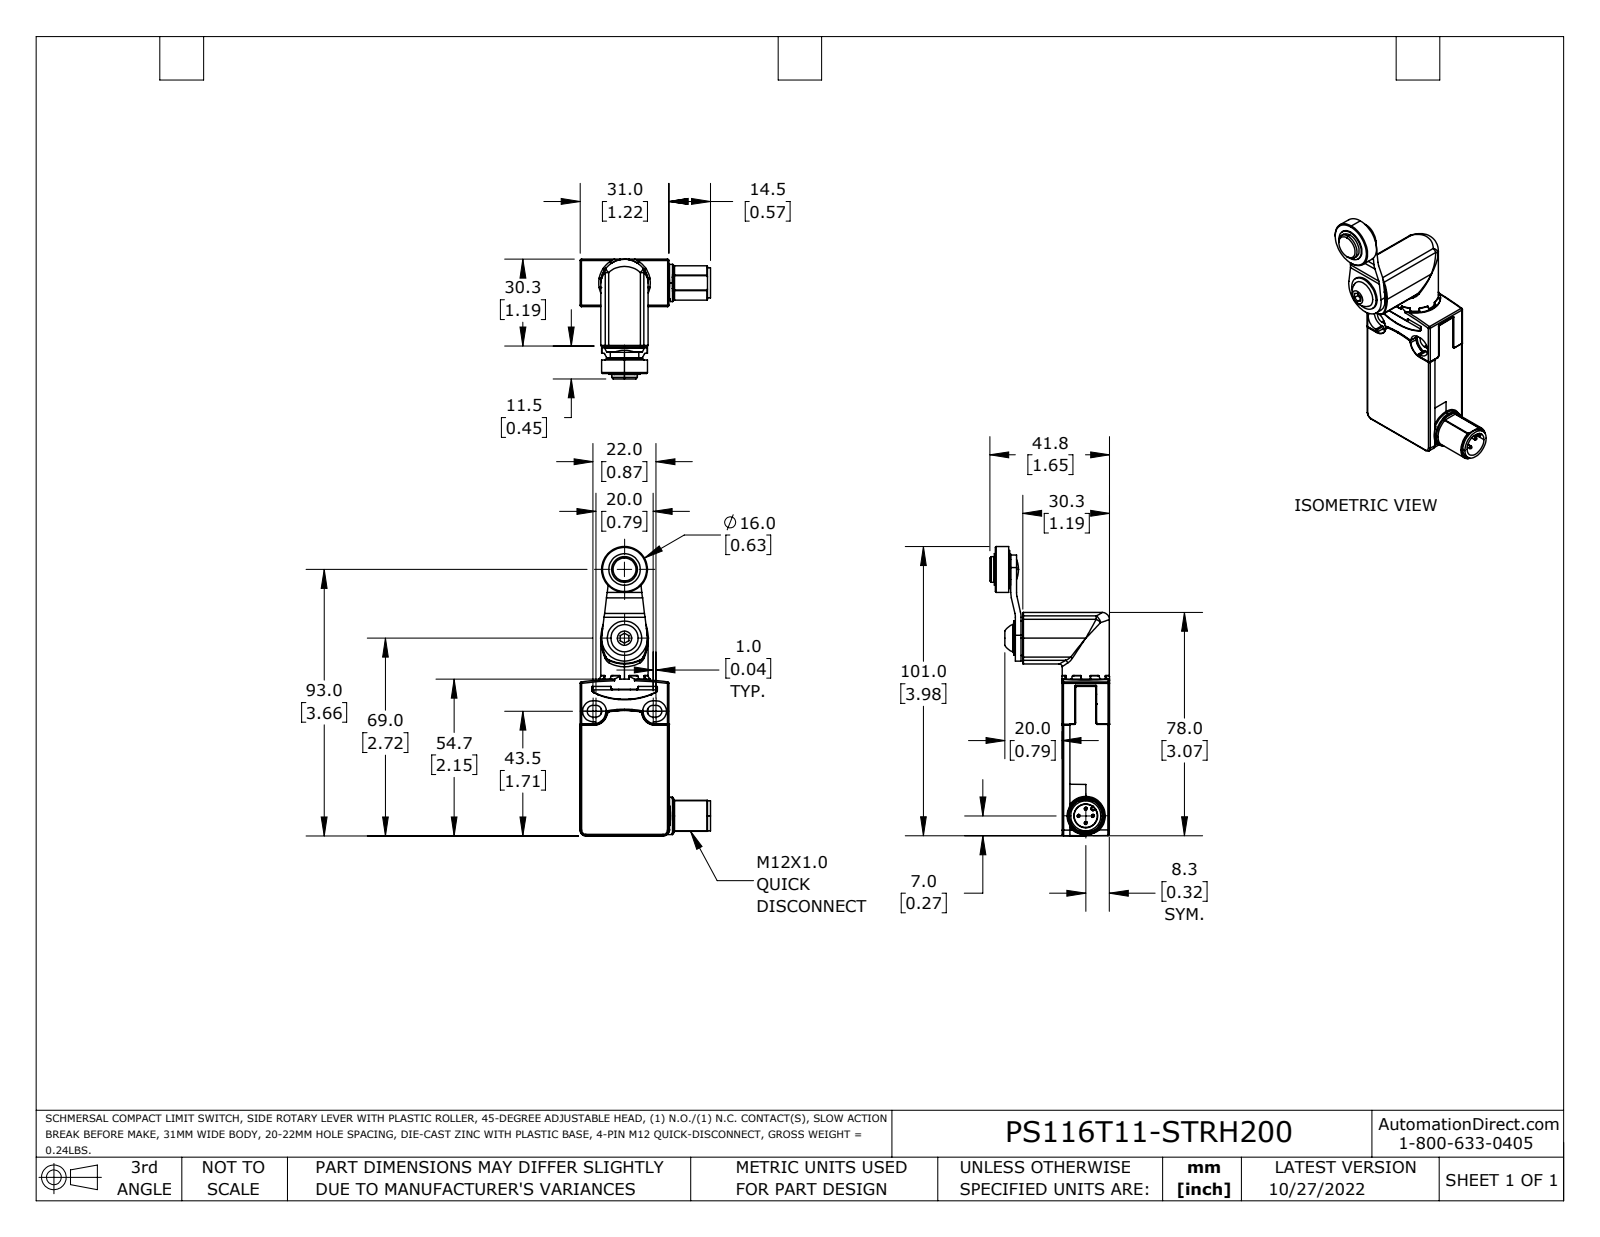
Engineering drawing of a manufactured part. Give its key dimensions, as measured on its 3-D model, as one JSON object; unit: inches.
{"part_name": "PS116T11-STRH200_Default", "step_written_by": "SolidWorks 2021 (CONFIG_CONTROL_DESIGN)", "units": "inches", "bodies": {"solids": 1, "faces": 957, "planar": 292, "cylindrical": 414, "other": 251}, "overall_size": [3.977, 1.791, 1.646], "volume_in3": 2.309, "surface_area_in2": 25.16, "round_holes": [[0.079, 1], [0.327, 1], [0.48, 1], [0.571, 1], [0.583, 1]], "round_bosses_or_shafts": [[0.039, 4], [0.512, 2], [0.65, 1], [0.63, 1], [0.567, 1], [0.524, 1], [0.475, 1], [0.472, 1]], "partial_cylinders_radius": [[0.008, 110], [0.004, 67], [0.02, 34], [0.014, 10], [0.039, 8], [0.079, 5], [0.081, 4], [0.098, 4]], "face_to_face_distances": [0.65, 0.652, 0.079, 1.22, 0.063, 0.118, 0.654, 0.016, 0.453, 0.291], "hole_center_spacings": [1.615]}
